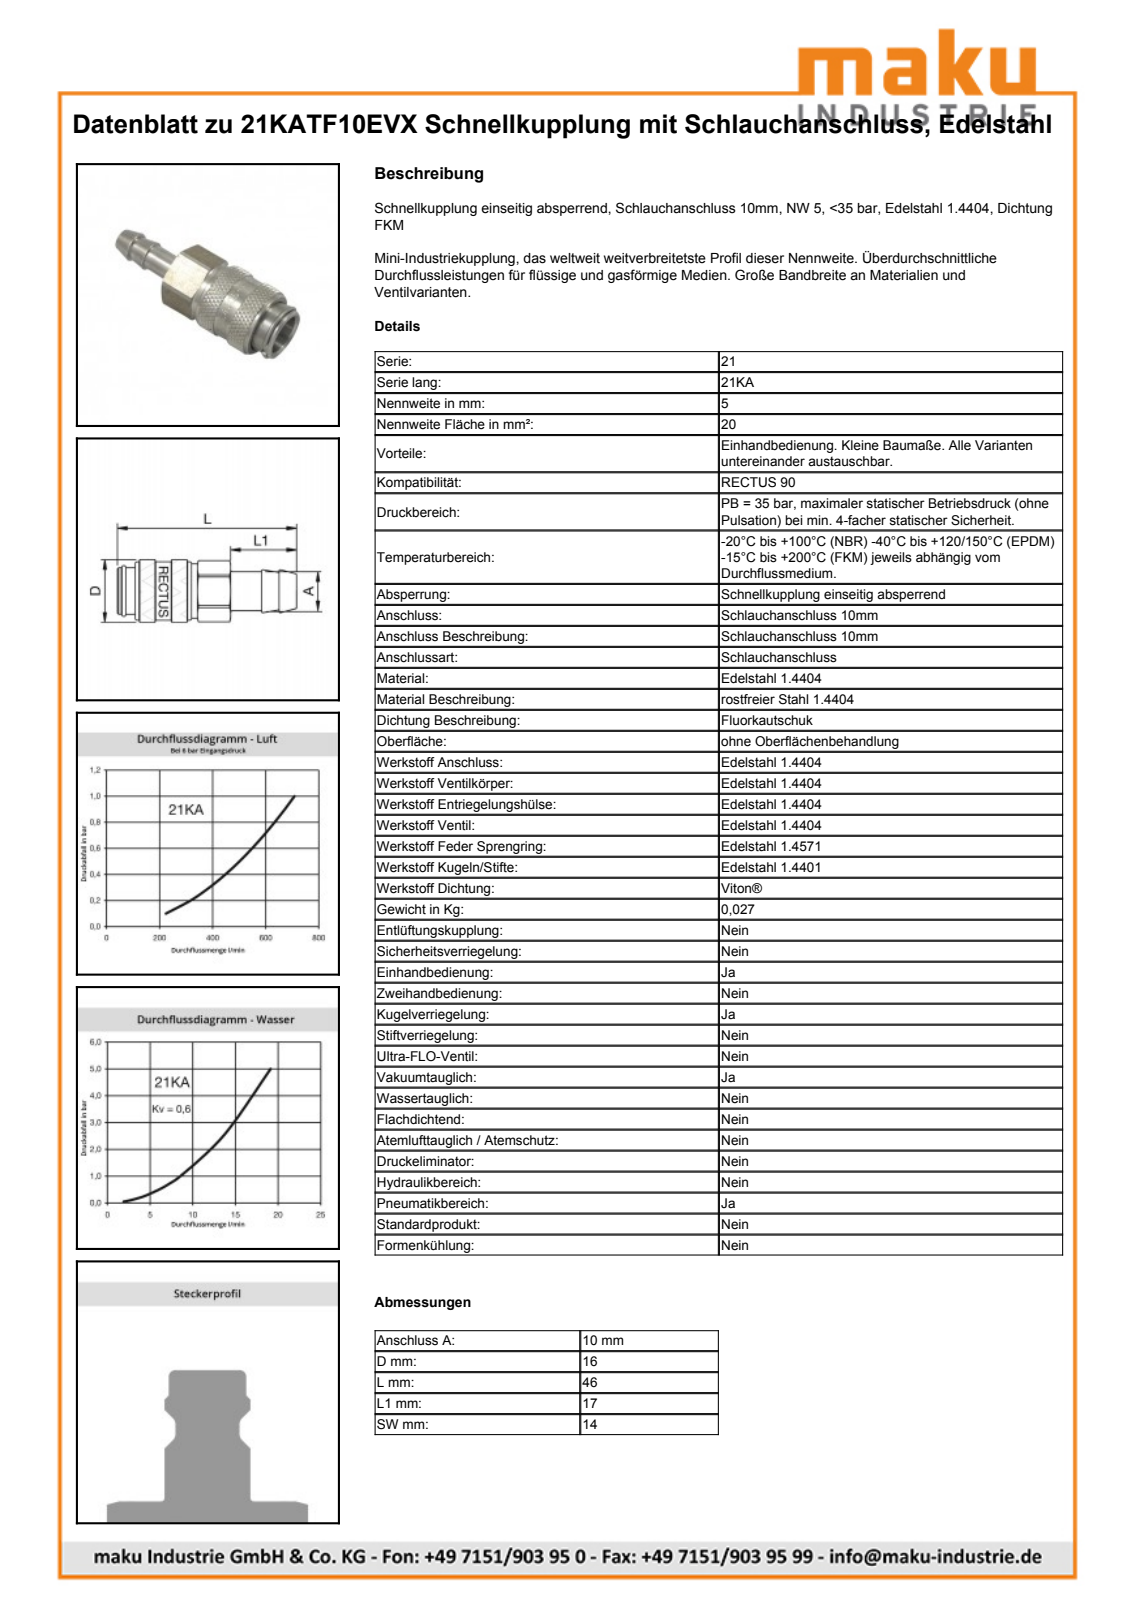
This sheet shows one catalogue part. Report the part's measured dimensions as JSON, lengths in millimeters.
{"part_name": "D110093", "step_written_by": "Autodesk Inventor 2013 (AUTOMOTIVE_DESIGN)", "units": "millimeters", "bodies": {"solids": 2, "faces": 399, "planar": 131, "cylindrical": 60, "other": 208}, "overall_size": [46.15, 16.15, 16.15], "volume_mm3": 6080, "surface_area_mm2": 3692, "round_holes": [[11.5, 1], [12.15, 1], [14, 1]], "round_bosses_or_shafts": [[16.15, 1], [15.1, 1], [12, 1], [11.4, 1], [11.15, 1], [10.05, 1]], "partial_cylinders_radius": [[5.53, 1], [7.45, 1], [7.9, 1]], "face_to_face_distances": [14, 29.15, 46.15, 17, 16.15, 13, 30, 4.56, 11.59, 24.59]}
